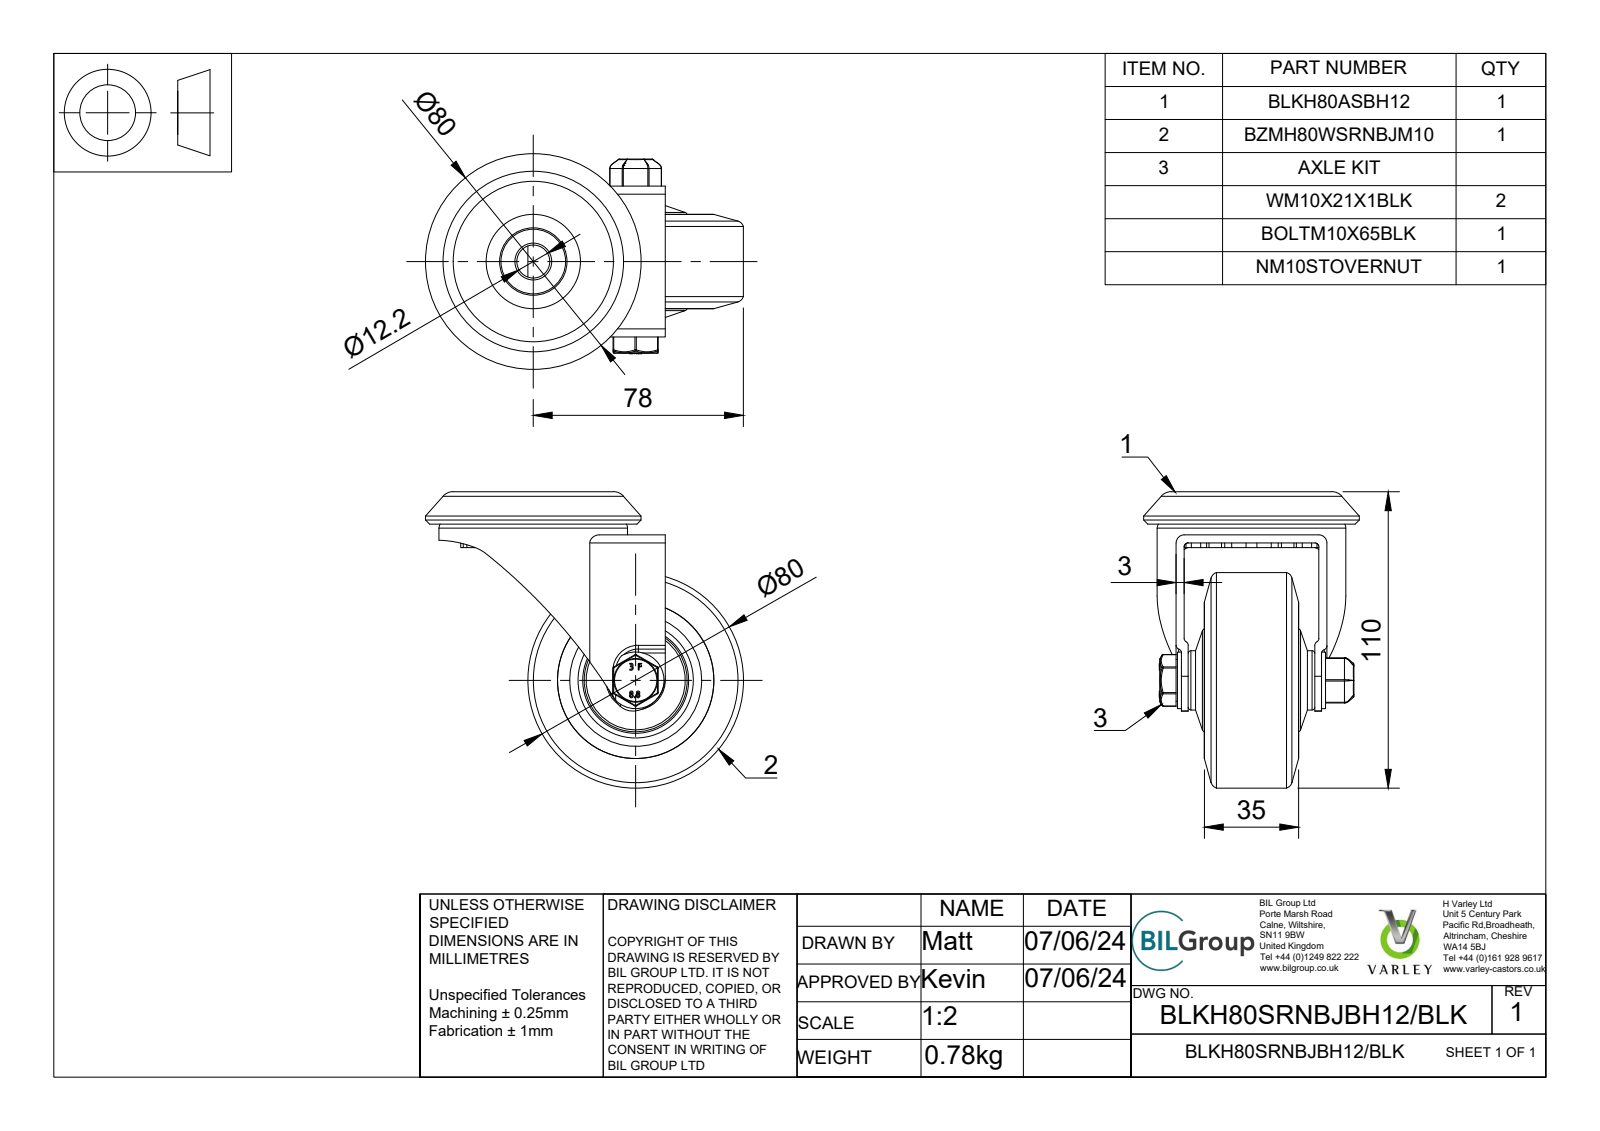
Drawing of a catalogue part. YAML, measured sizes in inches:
part_name: "BLKH80SRNBJBH12/BLK v3; BZMH80WSRNBJM10BLK v1; BZMH80WSRNBJBLK; 65 SHORE A GREY ELASTIC RUBBER TYRE (+6 more)"
step_written_by: "Autodesk Translation Framework v13.14.0.145 (AUTOMOTIVE_DESIGN)"
units: inches
bodies: {solids: 23, faces: 774, planar: 360, cylindrical: 220, other: 194}
overall_size: [4.646, 4.331, 3.15]
volume: 12.74
surface_area: 166.9
round_holes:
  - {diameter: 0.118, count: 6}
  - {diameter: 0.984, count: 2}
  - {diameter: 0.394, count: 1}
  - {diameter: 0.402, count: 1}
  - {diameter: 0.413, count: 1}
  - {diameter: 0.48, count: 1}
  - {diameter: 0.591, count: 1}
  - {diameter: 0.85, count: 1}
  - {diameter: 1.087, count: 1}
  - {diameter: 1.102, count: 1}
  - {diameter: 1.232, count: 1}
  - {diameter: 1.378, count: 1}
round_bosses_or_shafts:
  - {diameter: 3.15, count: 2}
  - {diameter: 2.756, count: 1}
  - {diameter: 2.126, count: 1}
  - {diameter: 1.685, count: 1}
  - {diameter: 1.506, count: 1}
  - {diameter: 1.35, count: 1}
  - {diameter: 1.197, count: 1}
  - {diameter: 1.165, count: 1}
partial_cylinders:
  - {radius: 0.059, count: 38}
  - {radius: 0.02, count: 12}
  - {radius: 0.013, count: 4}
  - {radius: 0.025, count: 4}
  - {radius: 0.006, count: 3}
  - {radius: 0.025, count: 3}
  - {radius: 0.191, count: 3}
  - {radius: 0.013, count: 2}
face_to_face_distances: [0.118, 0.059, 0.413, 0.472, 0.157, 0.098, 0.531, 2.087, 1.673, 1.791]
hole_center_spacings: [1.496]
